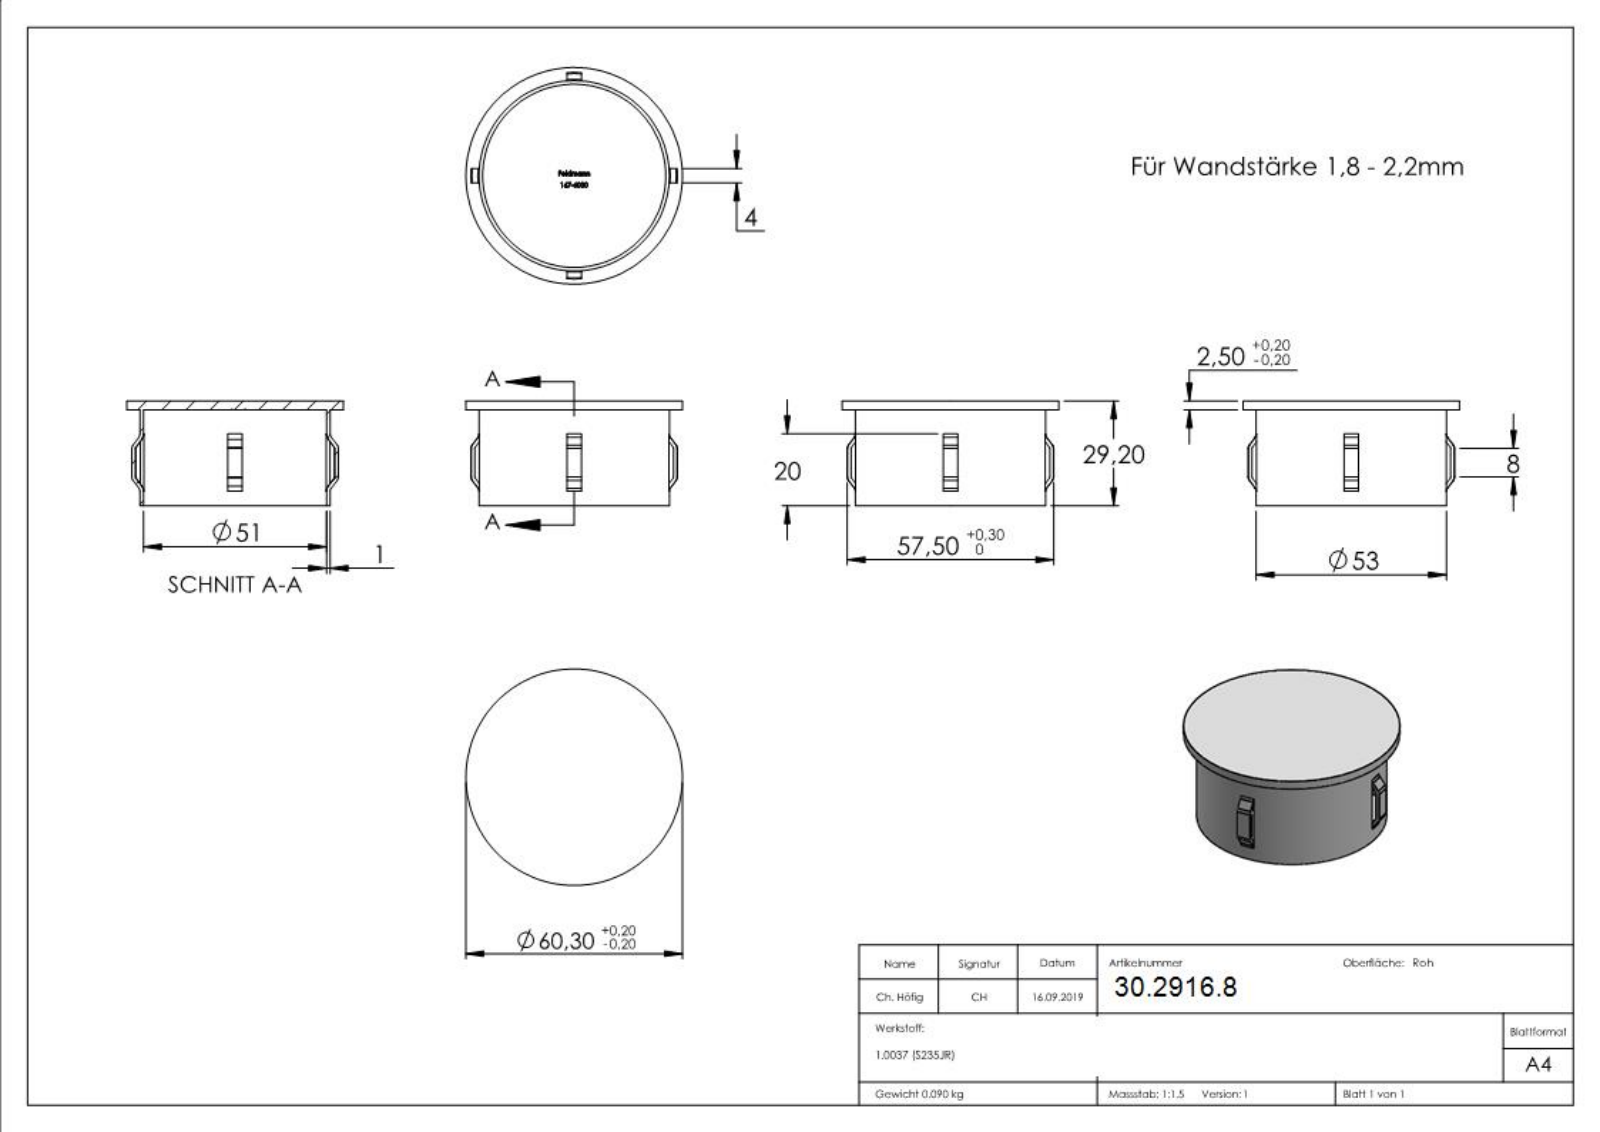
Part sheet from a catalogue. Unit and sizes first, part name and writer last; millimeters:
Units: millimetres
Overall size (bounding box): 60.3 × 60.3 × 29.2
Round holes (diameter × count): ⌀51 ×1
Round bosses / shafts (diameter × count): ⌀60.3 ×1, ⌀53 ×1
Partial cylindrical surfaces — rounded edges, fillets, slot ends (radius × count): R27.75 ×1, R28.75 ×1
Main face-to-face distances: 2.5, 26.7, 29.2, 4, 2.4, 26.8, 2.97, 1.26, 0.39, 2
Volume: 11 522 mm³ · Surface area: 15 183 mm²
Bodies: 1 solid, 289 faces (120 planar, 16 cylindrical, 153 other)
Part name (STEP PRODUCT): 167-6000
STEP written by: SolidWorks 2015 (CONFIG_CONTROL_DESIGN)
